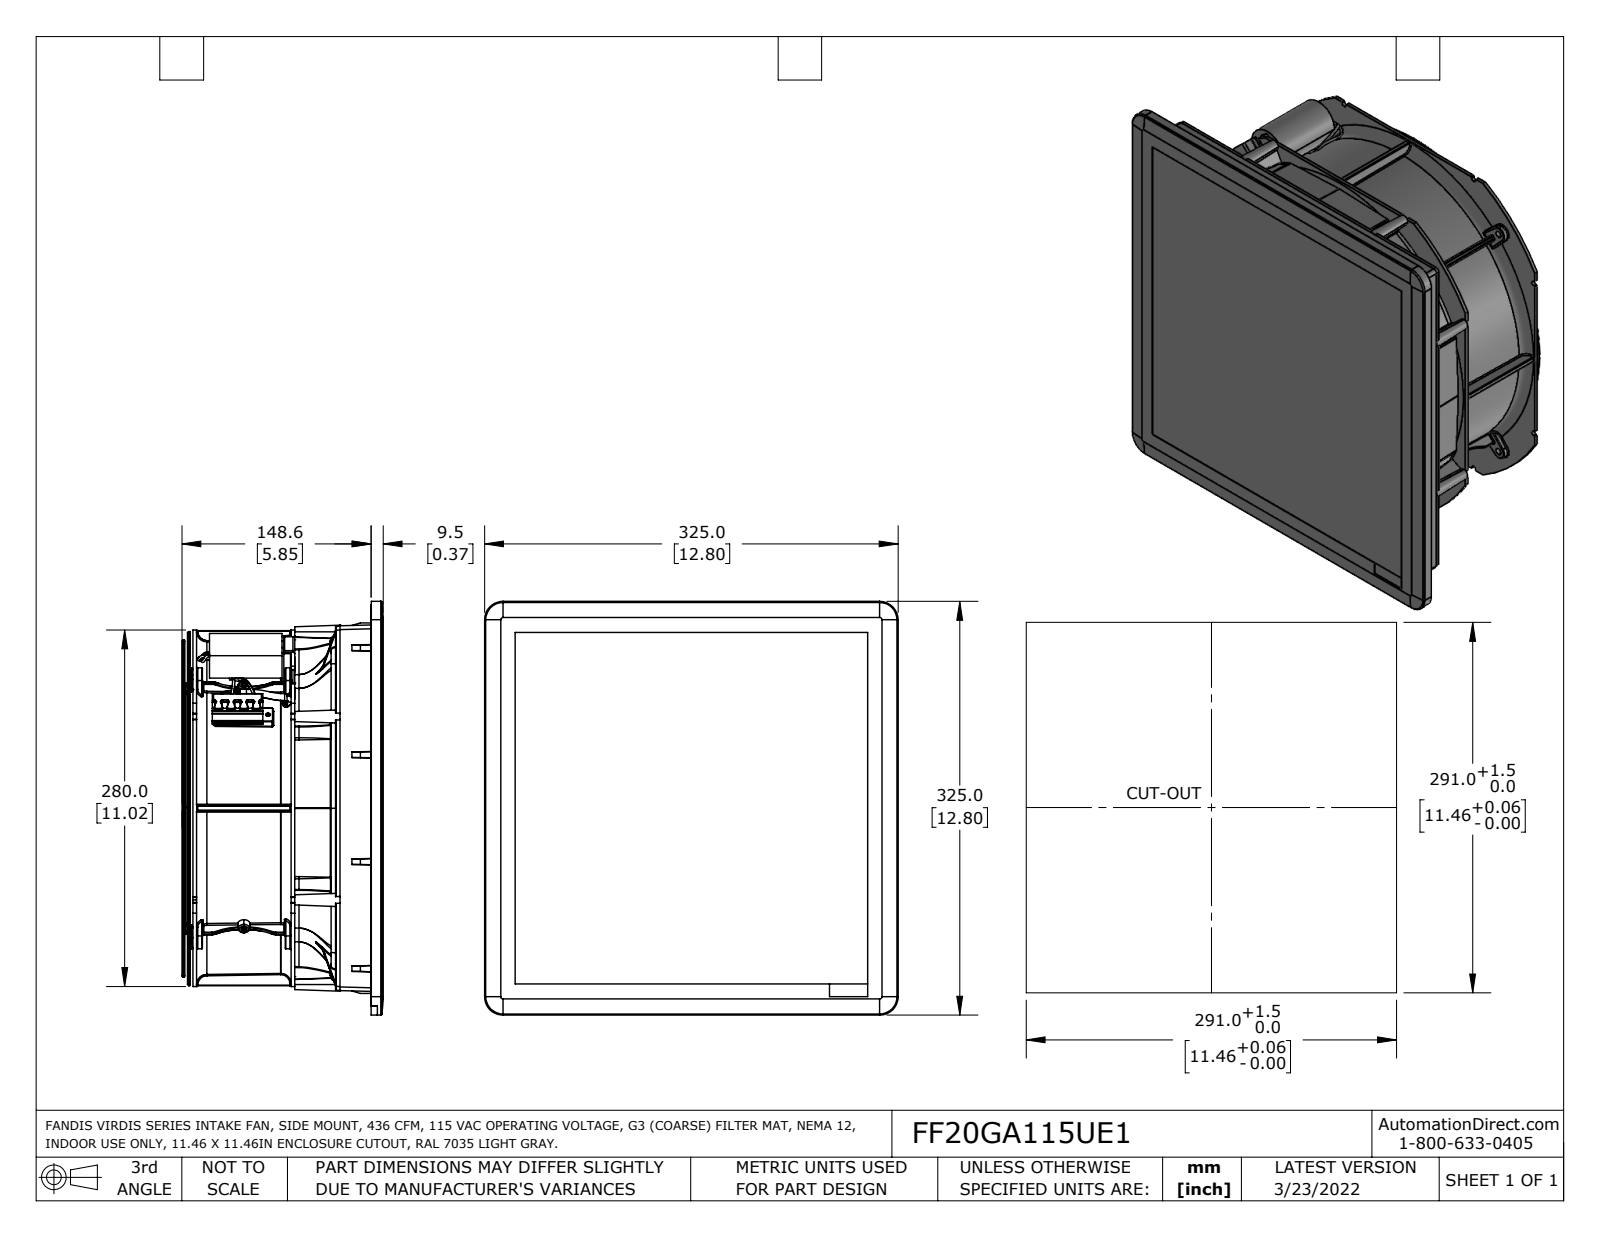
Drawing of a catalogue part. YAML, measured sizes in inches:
part_name: "FF20GA115UE1"
step_written_by: "SolidWorks 2021 (AUTOMOTIVE_DESIGN)"
units: inches
bodies: {solids: 7, faces: 2194, planar: 452, cylindrical: 571, other: 1171}
overall_size: [12.795, 12.795, 6.226]
volume: 599.6
surface_area: 810.4
round_holes:
  - {diameter: 0.177, count: 8}
  - {diameter: 0.213, count: 4}
  - {diameter: 0.108, count: 3}
  - {diameter: 0.13, count: 2}
round_bosses_or_shafts:
  - {diameter: 0.091, count: 24}
  - {diameter: 0.051, count: 8}
  - {diameter: 0.079, count: 4}
  - {diameter: 0.217, count: 3}
  - {diameter: 1.378, count: 1}
  - {diameter: 0.315, count: 1}
partial_cylinders:
  - {radius: 0.02, count: 124}
  - {radius: 0.039, count: 72}
  - {radius: 0.157, count: 31}
  - {radius: 0.059, count: 12}
  - {radius: 0.079, count: 10}
  - {radius: 0.016, count: 9}
  - {radius: 0.01, count: 8}
  - {radius: 0.047, count: 8}
face_to_face_distances: [5.874, 0.11, 3.039, 5.512, 0.362, 2.736, 0.374, 5.886, 2.835, 2.724]
hole_center_spacings: [1.852, 7.07, 8.691, 9.643, 11.813, 3.703, 5.669, 8.213]
